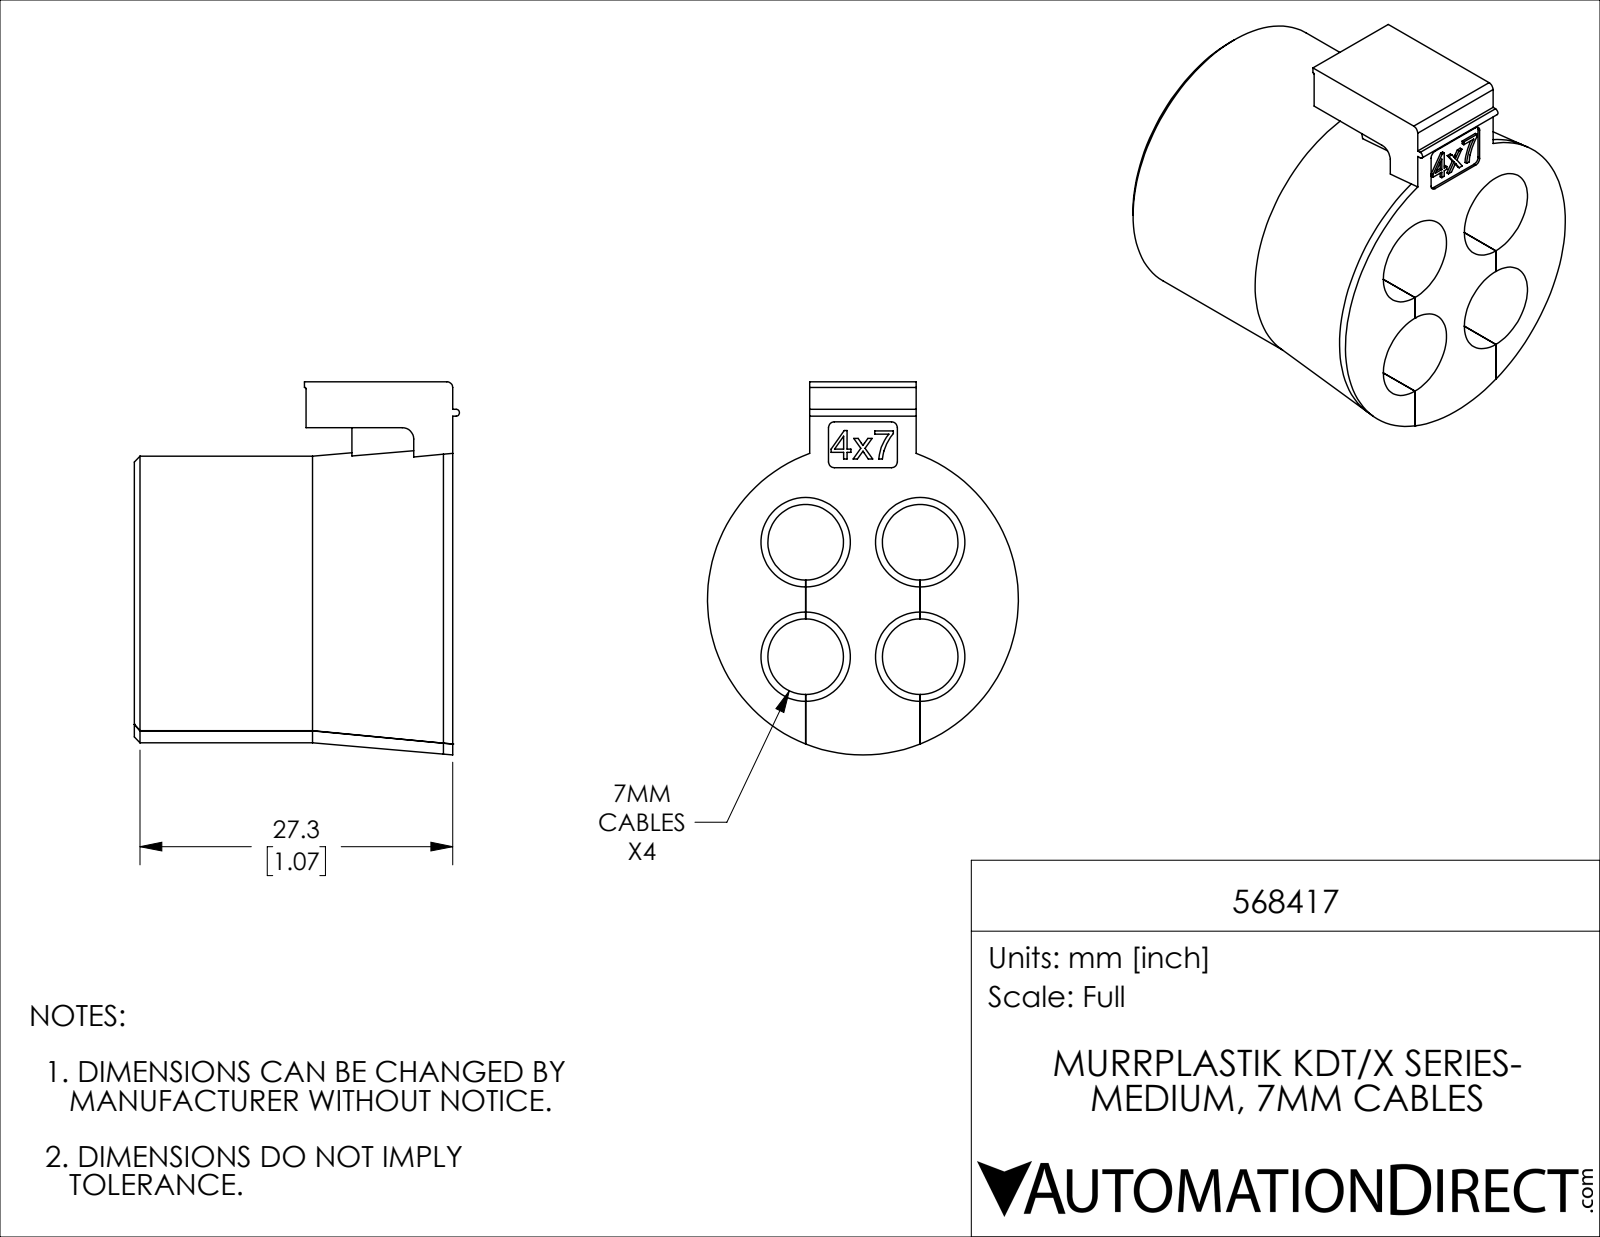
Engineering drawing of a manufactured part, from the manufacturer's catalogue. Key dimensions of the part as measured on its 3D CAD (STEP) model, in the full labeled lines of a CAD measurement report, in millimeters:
Part name (STEP PRODUCT): 568417
STEP written by: SolidWorks 2019 (CONFIG_CONTROL_DESIGN)
Units: millimetres
Bodies: 1 solid, 155 faces (66 planar, 50 cylindrical, 39 other)
Overall size (bounding box): 32.6 × 28.4 × 27.2
Volume: 9 490 mm³ · Surface area: 6 613 mm²
Round holes (diameter × count): ⌀6.6 ×4, ⌀7.8 ×4
Round bosses / shafts (diameter × count): ⌀25 ×1
Partial cylindrical surfaces — rounded edges, fillets, slot ends (radius × count): R0.5 ×5, R0.1 ×1, R0.3 ×1, R1 ×1
Main face-to-face distances: 10, 27.8, 10, 10, 0.3, 0.4, 9.7, 9.7, 4, 9.3
Hole centre spacings: 10, 14.1
